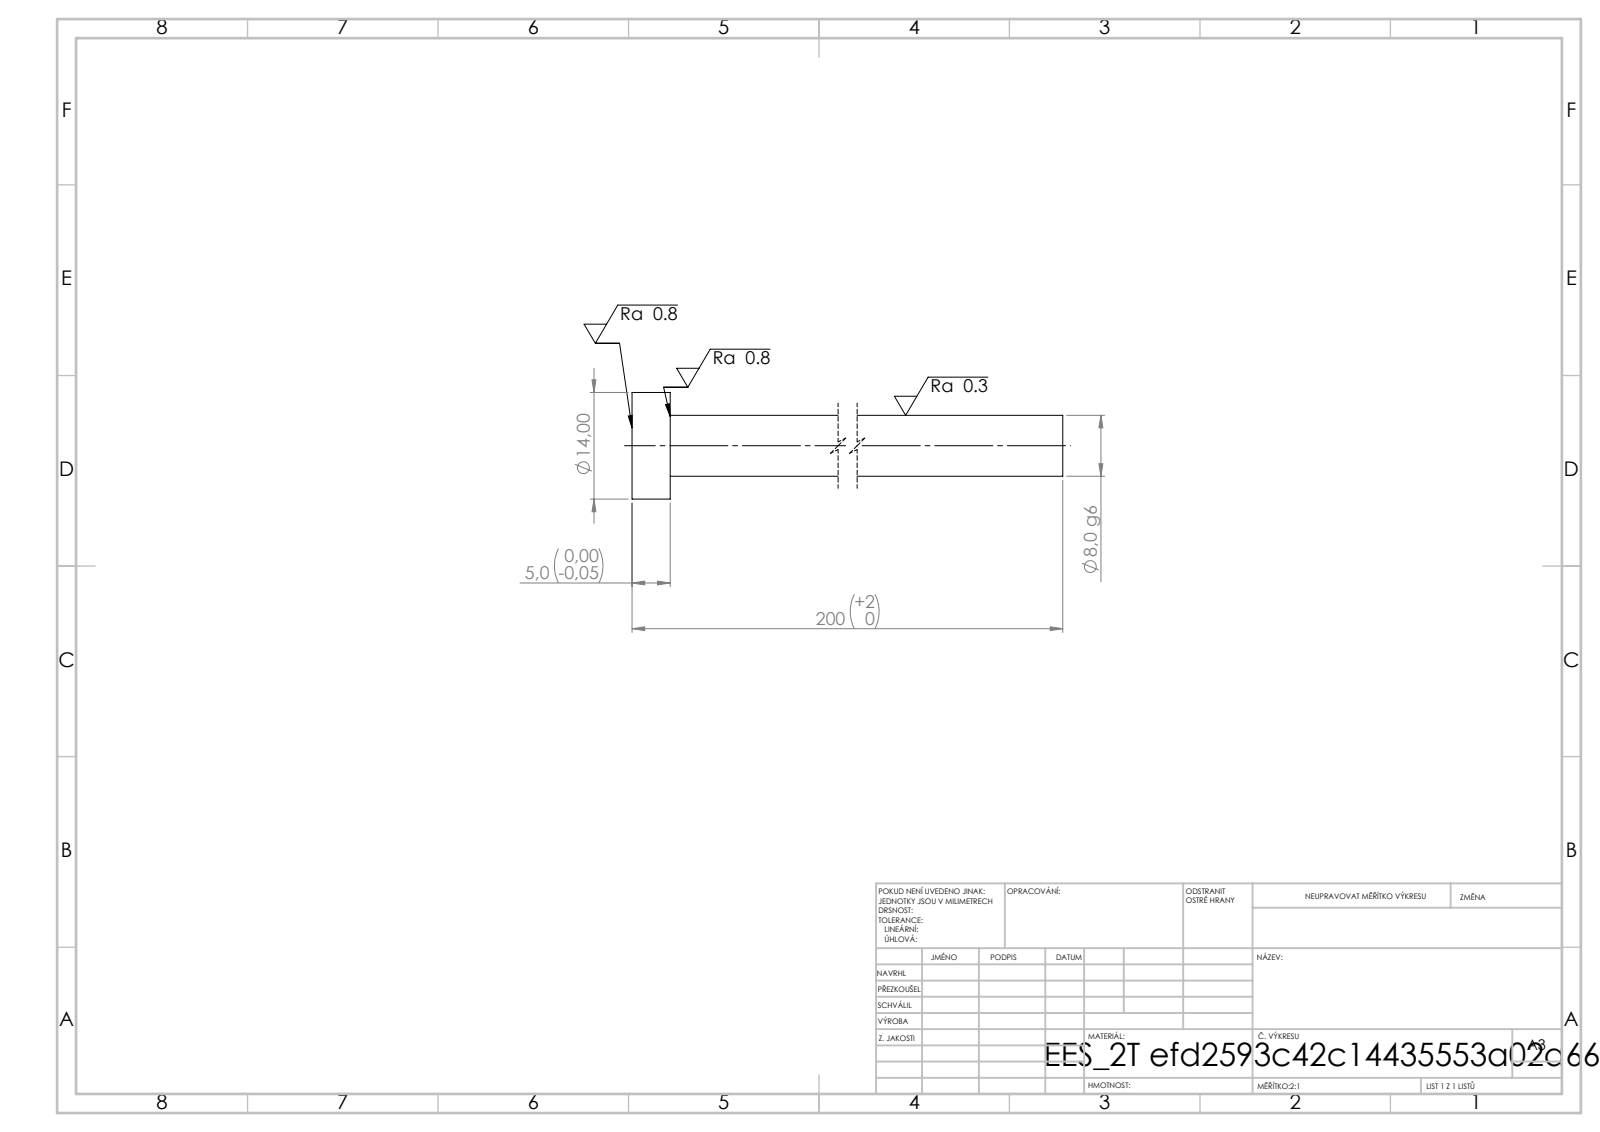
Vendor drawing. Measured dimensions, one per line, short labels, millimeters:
written by: SolidWorks 2019 (CONFIG_CONTROL_DESIGN)
unit: mm
bodies: 1 solid, 7 faces (3 planar, 4 cylindrical, 0 other)
size: 200 × 14 × 14
volume: 10 571 mm³; area: 5 429 mm²
bosses: 1× ⌀14, 1× ⌀8
face distances: 5, 200, 195
